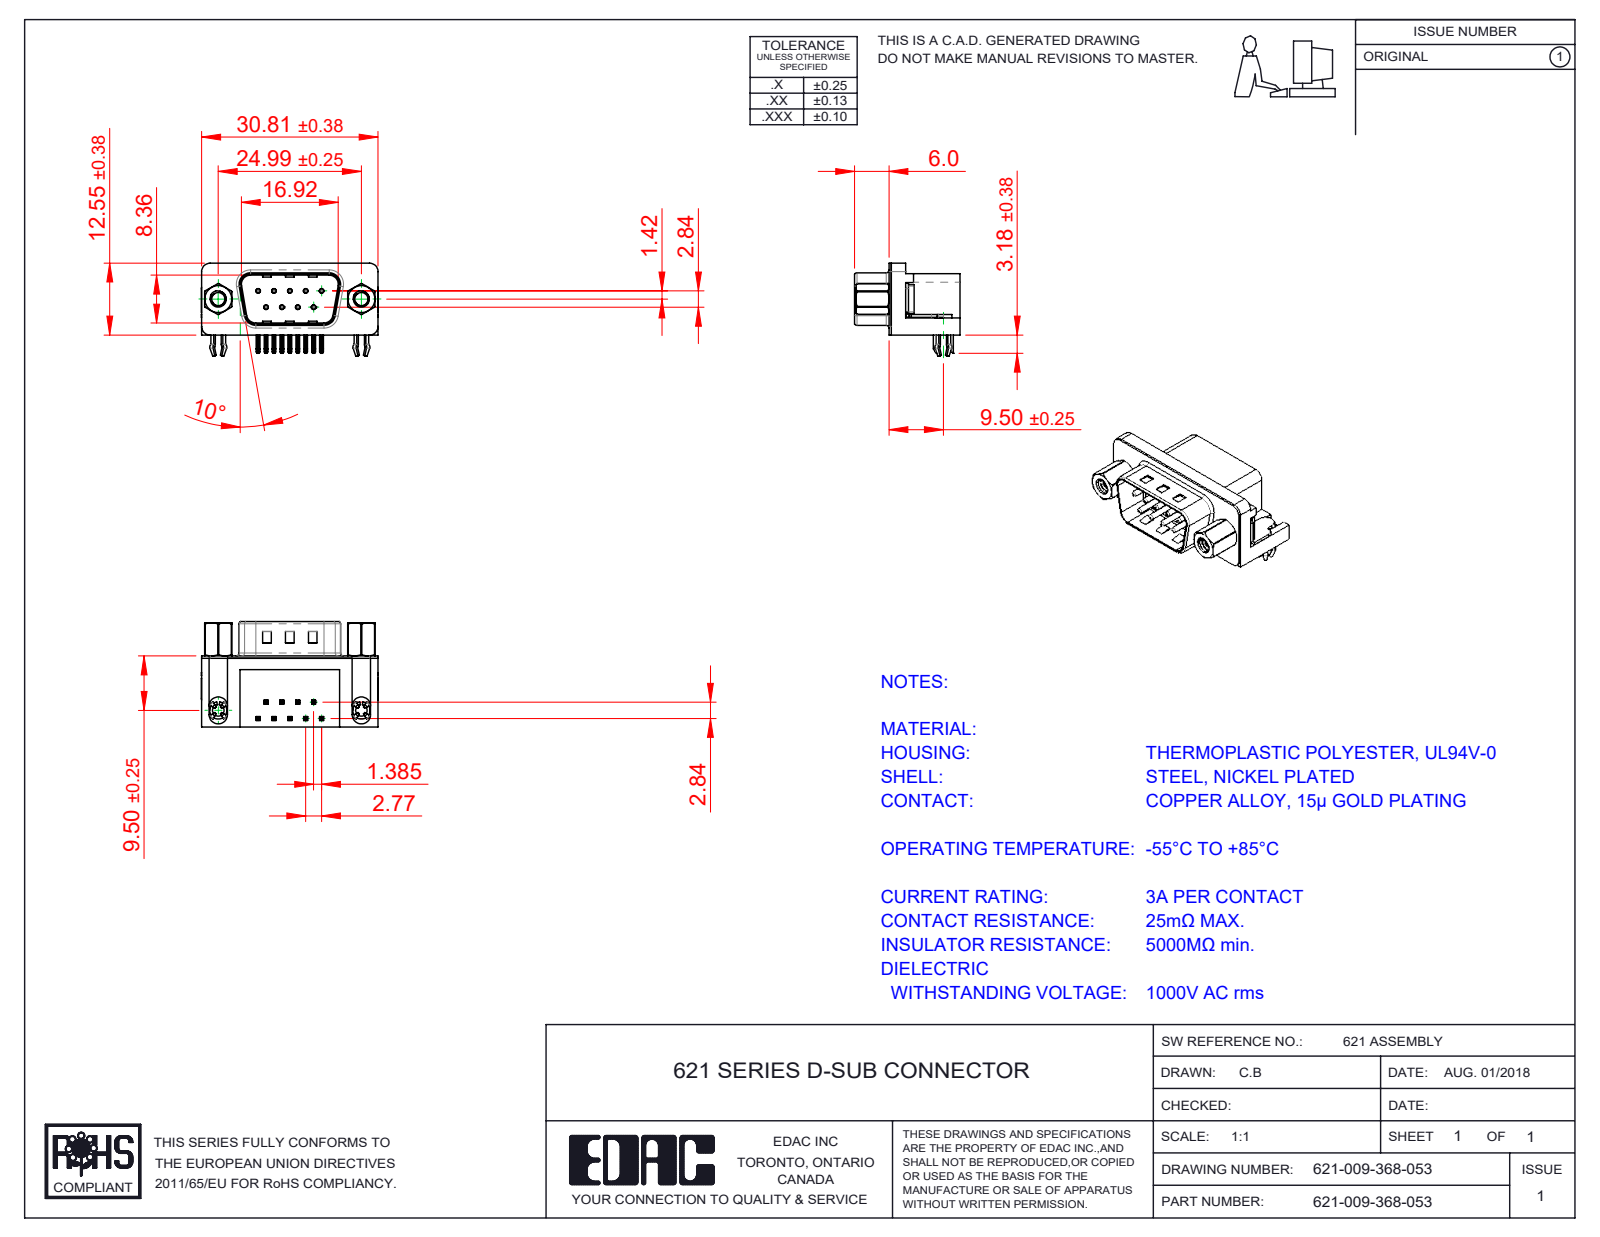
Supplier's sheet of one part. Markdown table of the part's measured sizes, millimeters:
| quantity | value |
| --- | --- |
| part name | 621 4-40 Hex Standoff 5; 621 4-40 Threaded Board Mount; 621 Contact Top; 621 Contact Bottom (+4 more) |
| STEP written by | SolidWorks 2016 (CONFIG_CONTROL_DESIGN) |
| units | millimeters |
| bodies | 17 solids, 1147 faces (595 planar, 399 cylindrical, 153 other) |
| overall size | 30.89 × 18.4 × 15.73 |
| volume | 3 471 mm³ |
| surface area | 4 983 mm² |
| round holes (diameter × count) | 0.35 × 9, 0.8 × 9, 2.26 × 4, 2.29 × 2, 4 × 2, 4.8 × 2, 5 × 2 |
| round bosses / shafts (diameter × count) | 0.75 × 9, 4.9 × 2, 4.75 × 2, 3.9 × 2, 3.26 × 2, 2.79 × 2 |
| partial cylindrical surfaces (radius × count) | 0.25 × 44, 0.12 × 18, 1 × 16, 0.5 × 9, 1.5 × 8, 1.6 × 8, 0.9 × 4, 2 × 4 |
| main face-to-face distances | 0.4, 12, 12.4, 10.35, 9.5, 2.5, 2.9, 0.5, 2.1, 0.35 |
| hole center spacings | 3.16, 2.77, 5.54, 5.03, 5.04, 8.31, 7.48, 7.49 |
